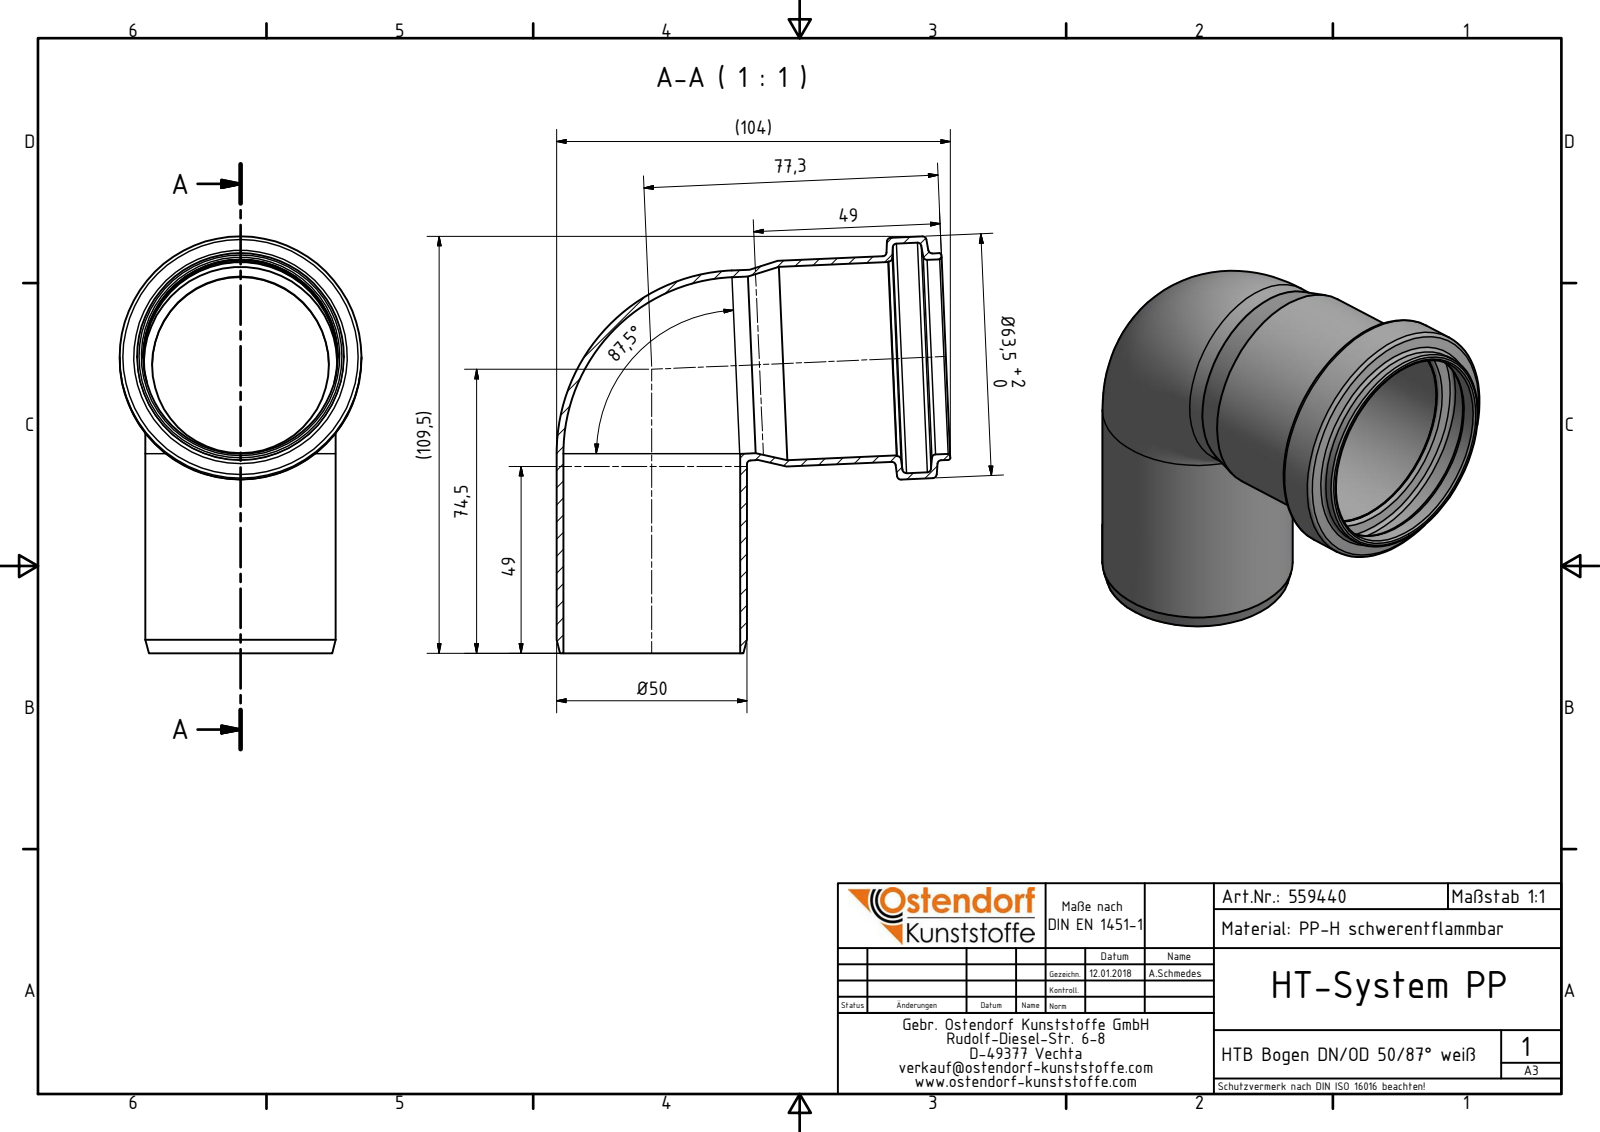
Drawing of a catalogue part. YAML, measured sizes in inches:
part_name: "559440 HTB DN_OD 50_87° weiß"
step_written_by: "Autodesk Inventor 2016 (AUTOMOTIVE_DESIGN)"
units: inches
bodies: {solids: 1, faces: 34, planar: 3, cylindrical: 11, other: 20}
overall_size: [4.307, 4.07, 2.5]
volume: 2.344
surface_area: 74.45
round_holes:
  - {diameter: 1.827, count: 2}
  - {diameter: 2, count: 1}
  - {diameter: 2.012, count: 1}
  - {diameter: 2.374, count: 1}
round_bosses_or_shafts:
  - {diameter: 1.969, count: 2}
  - {diameter: 2.5, count: 1}
  - {diameter: 2.138, count: 1}
  - {diameter: 2.126, count: 1}
face_to_face_distances: [0.553]
